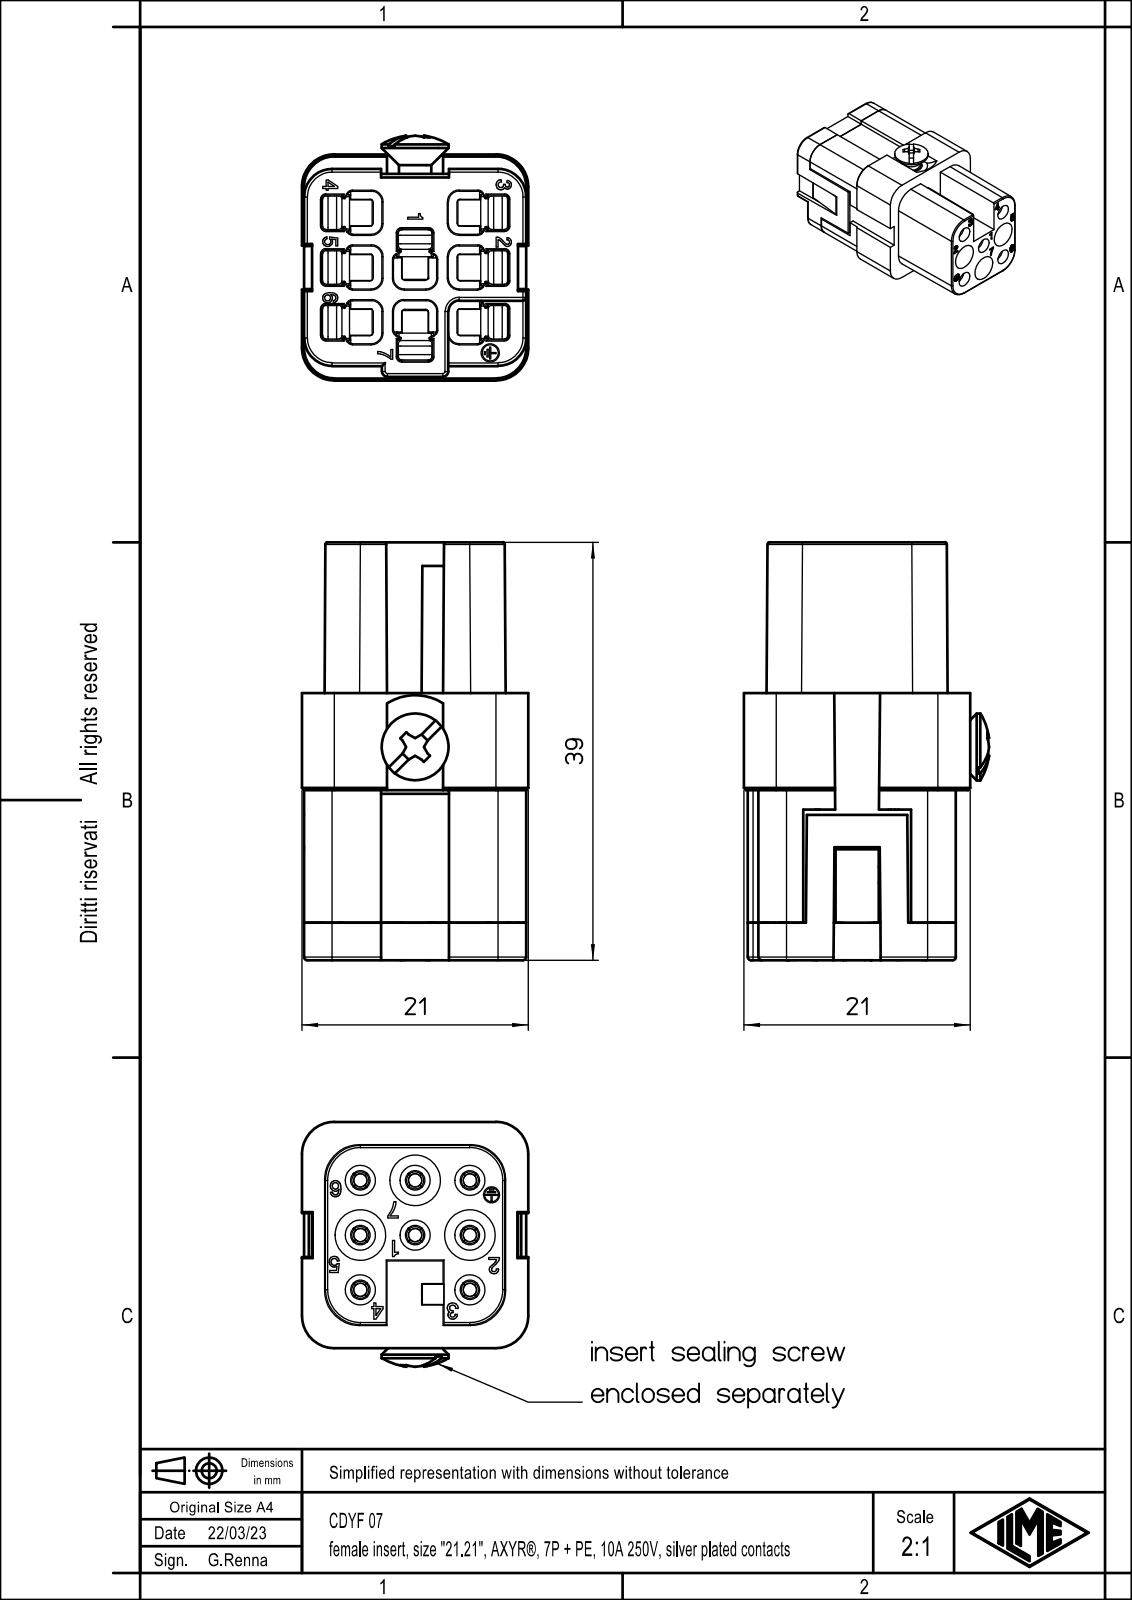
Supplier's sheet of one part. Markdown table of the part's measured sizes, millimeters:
| quantity | value |
| --- | --- |
| part name | CDYF 07 |
| STEP written by | Creo Elements/Direct Modeling 20.1B 02-Apr-2019 (C) Parametric Technology GmbH (AUTOMOTIVE_DESIGN) |
| units | millimeters |
| bodies | 1 solid, 1524 faces (839 planar, 397 cylindrical, 288 other) |
| overall size | 38.8 × 22.72 × 21 |
| volume | 11 734 mm³ |
| surface area | 7 217 mm² |
| round holes (diameter × count) | 1.7 × 8, 1.8 × 8, 2.8 × 5, 4.7 × 3, 1.5 × 1, 2.5 × 1, 4 × 1 |
| round bosses / shafts (diameter × count) | 2.5 × 8, 6.2 × 1, 3.8 × 1, 3 × 1, 1.3 × 1 |
| partial cylindrical surfaces (radius × count) | 0.1 × 63, 0.3 × 43, 0.2 × 36, 0.5 × 20, 0.4 × 16, 1 × 16, 1.5 × 5, 2.6 × 4 |
| main face-to-face distances | 0.8, 1, 19.8, 19.65, 1.35, 20.8, 20, 21, 24.8, 3.5 |
| hole center spacings | 5.08, 7.18, 11.36, 10.16, 14.37, 2.42, 4.24, 7.22 |
